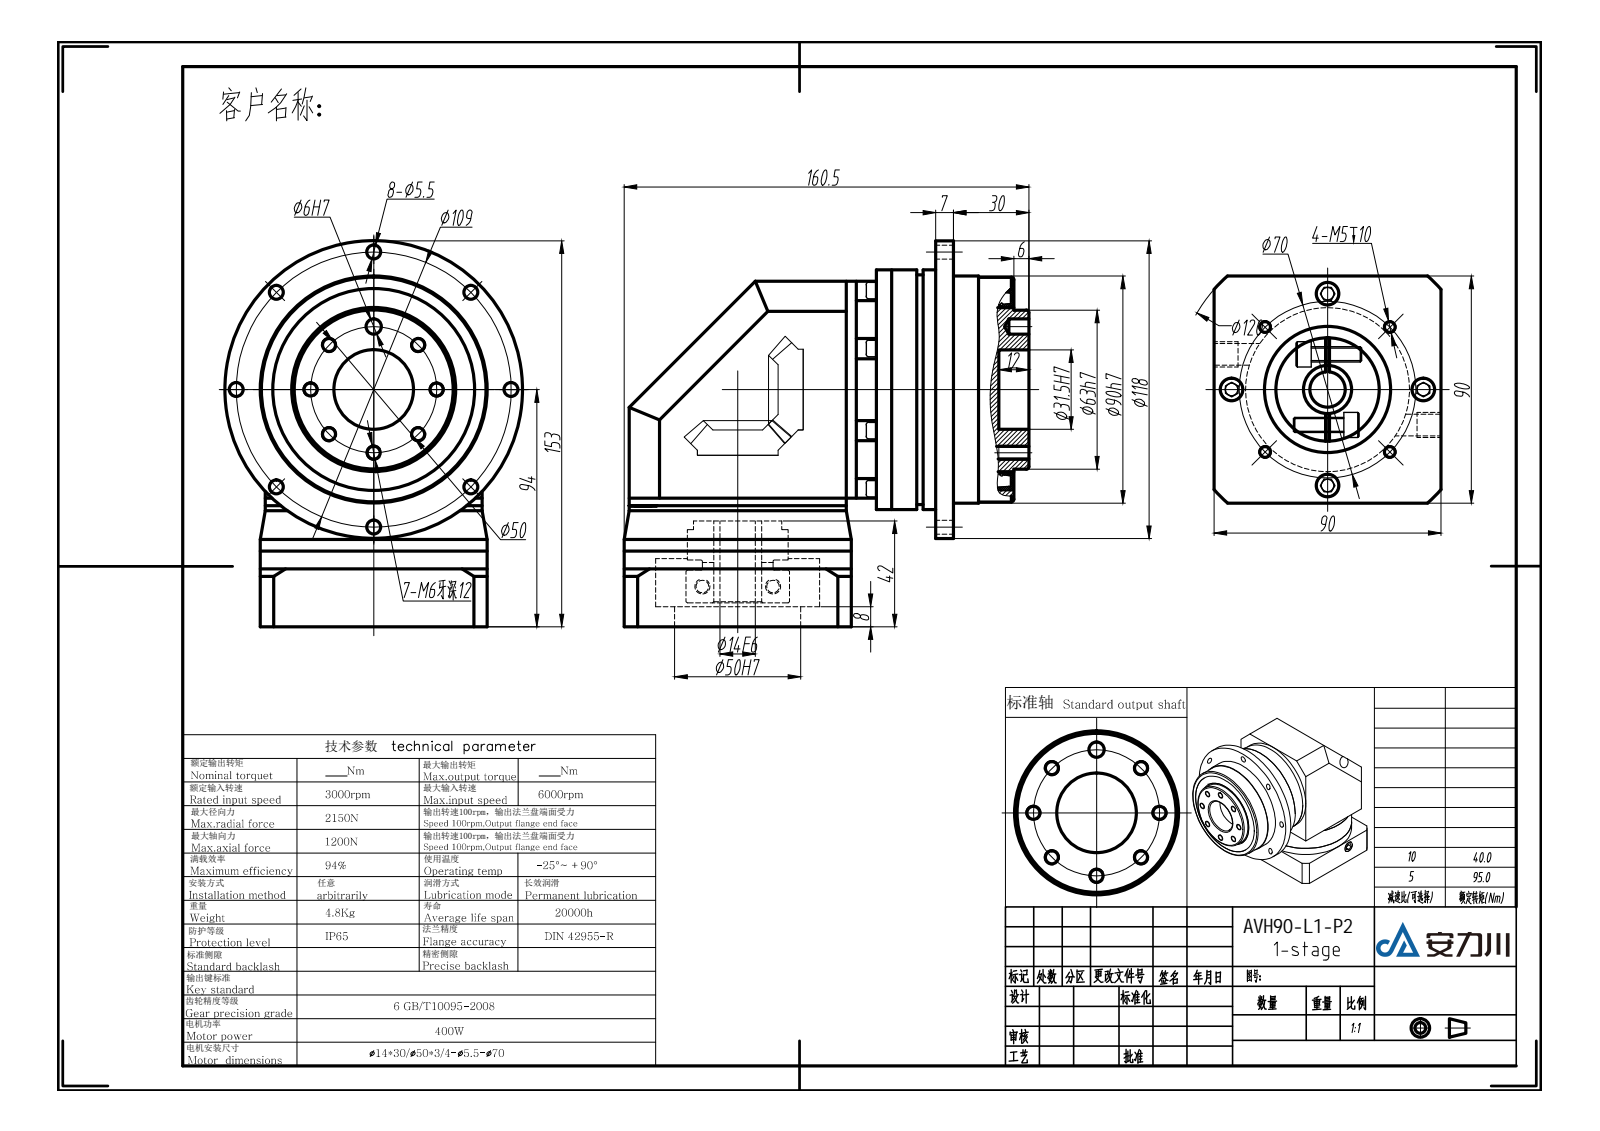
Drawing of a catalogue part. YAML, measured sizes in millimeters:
part_name: "VGZH90单级模型（14-30 50-3 4-5.5-70）"
step_written_by: "SolidWorks 2016 (AUTOMOTIVE_DESIGN)"
units: millimeters
bodies: {solids: 6, faces: 481, planar: 246, cylindrical: 201, other: 34}
overall_size: [160.5, 153, 118]
volume: 1239000
surface_area: 173370
round_holes:
  - {diameter: 5.5, count: 8}
  - {diameter: 10, count: 8}
  - {diameter: 5, count: 7}
  - {diameter: 4.2, count: 4}
  - {diameter: 9, count: 4}
  - {diameter: 6, count: 1}
  - {diameter: 14, count: 1}
  - {diameter: 19, count: 1}
  - {diameter: 20, count: 1}
  - {diameter: 31.5, count: 1}
  - {diameter: 50, count: 1}
  - {diameter: 65, count: 1}
round_bosses_or_shafts:
  - {diameter: 7, count: 8}
  - {diameter: 8.5, count: 6}
  - {diameter: 8.4, count: 4}
  - {diameter: 90, count: 2}
  - {diameter: 86, count: 2}
  - {diameter: 9.8, count: 2}
  - {diameter: 118, count: 1}
  - {diameter: 95, count: 1}
partial_cylinders:
  - {radius: 1, count: 16}
  - {radius: 4, count: 8}
  - {radius: 60, count: 1}
face_to_face_distances: [18, 14, 2, 30, 86, 88, 90, 48, 38.5, 7]
hole_center_spacings: [74.31, 17.71, 24.24, 52.88, 53.19, 90.78, 38, 19.14]
